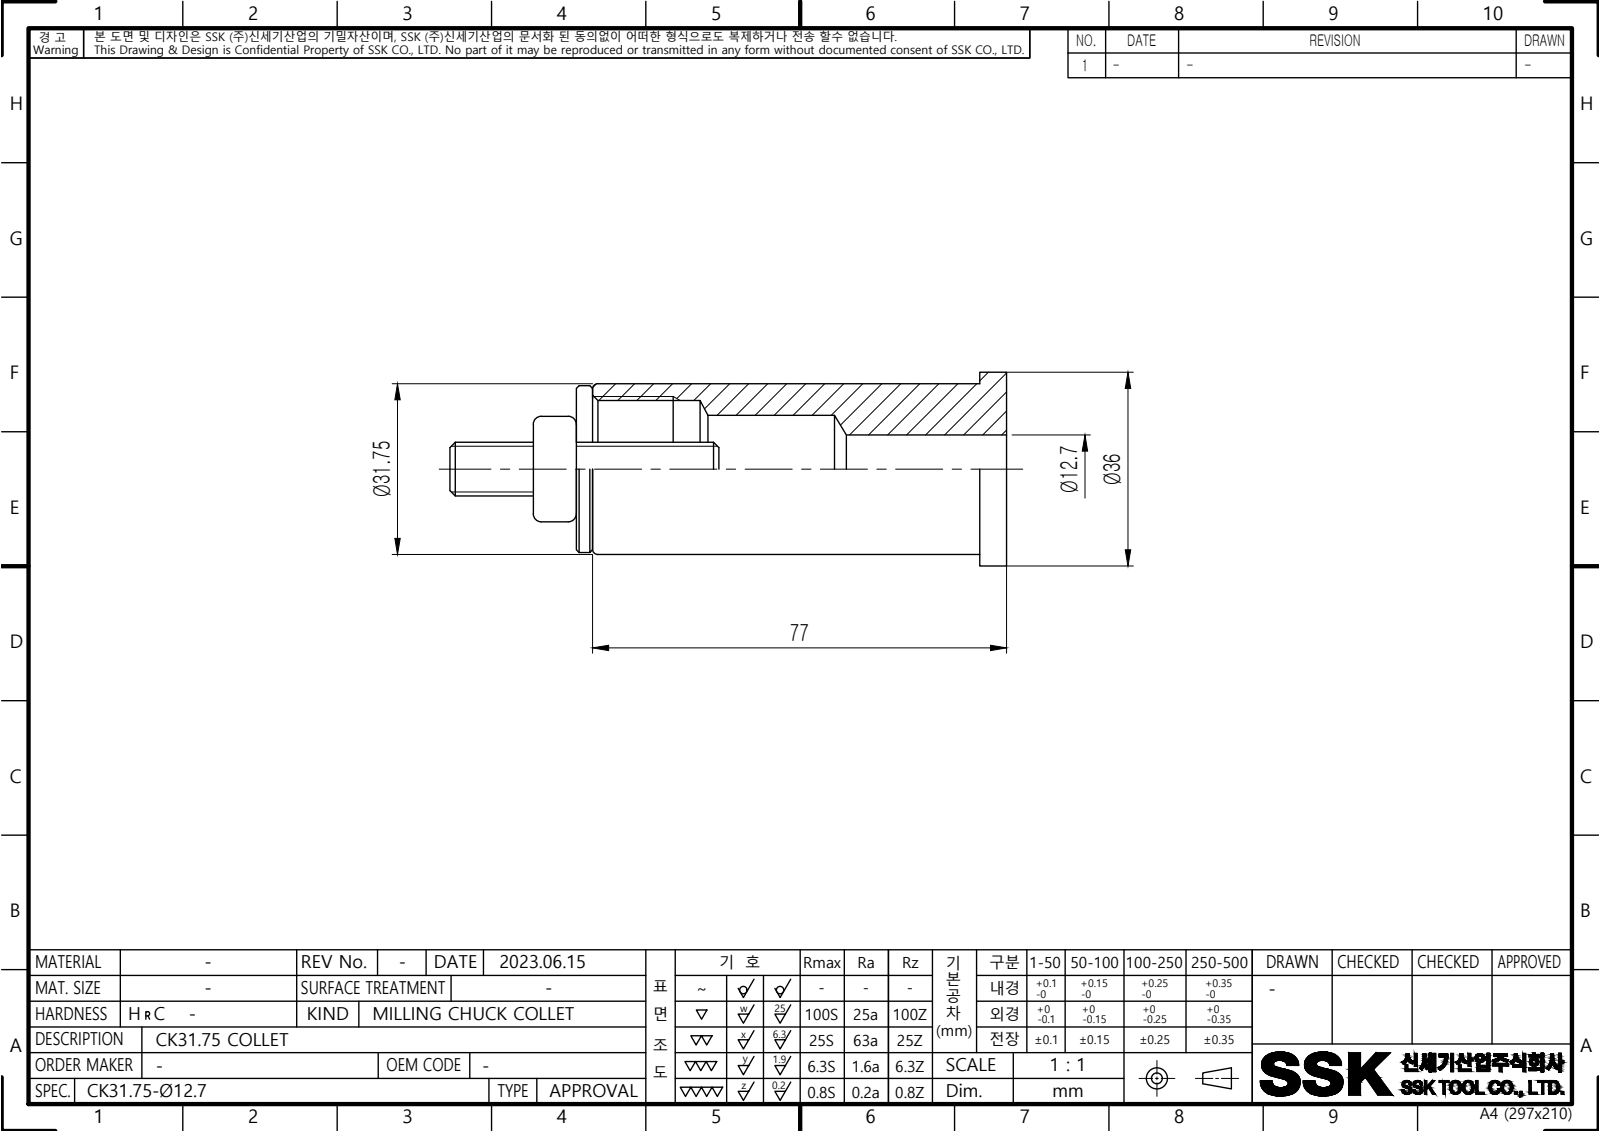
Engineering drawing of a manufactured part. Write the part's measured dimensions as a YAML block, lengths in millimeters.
part_name: "LO-CK31.75-12.7"
step_written_by: "Autodesk Inventor 2022 (AUTOMOTIVE_DESIGN)"
units: millimeters
bodies: {solids: 1, faces: 10, planar: 3, cylindrical: 5, other: 2}
overall_size: [77, 36, 36]
volume: 39732
surface_area: 13846
round_holes:
  - {diameter: 12.7, count: 1}
  - {diameter: 20, count: 1}
  - {diameter: 25.38, count: 1}
round_bosses_or_shafts:
  - {diameter: 36, count: 1}
  - {diameter: 31.75, count: 1}
face_to_face_distances: [77, 72, 5]
